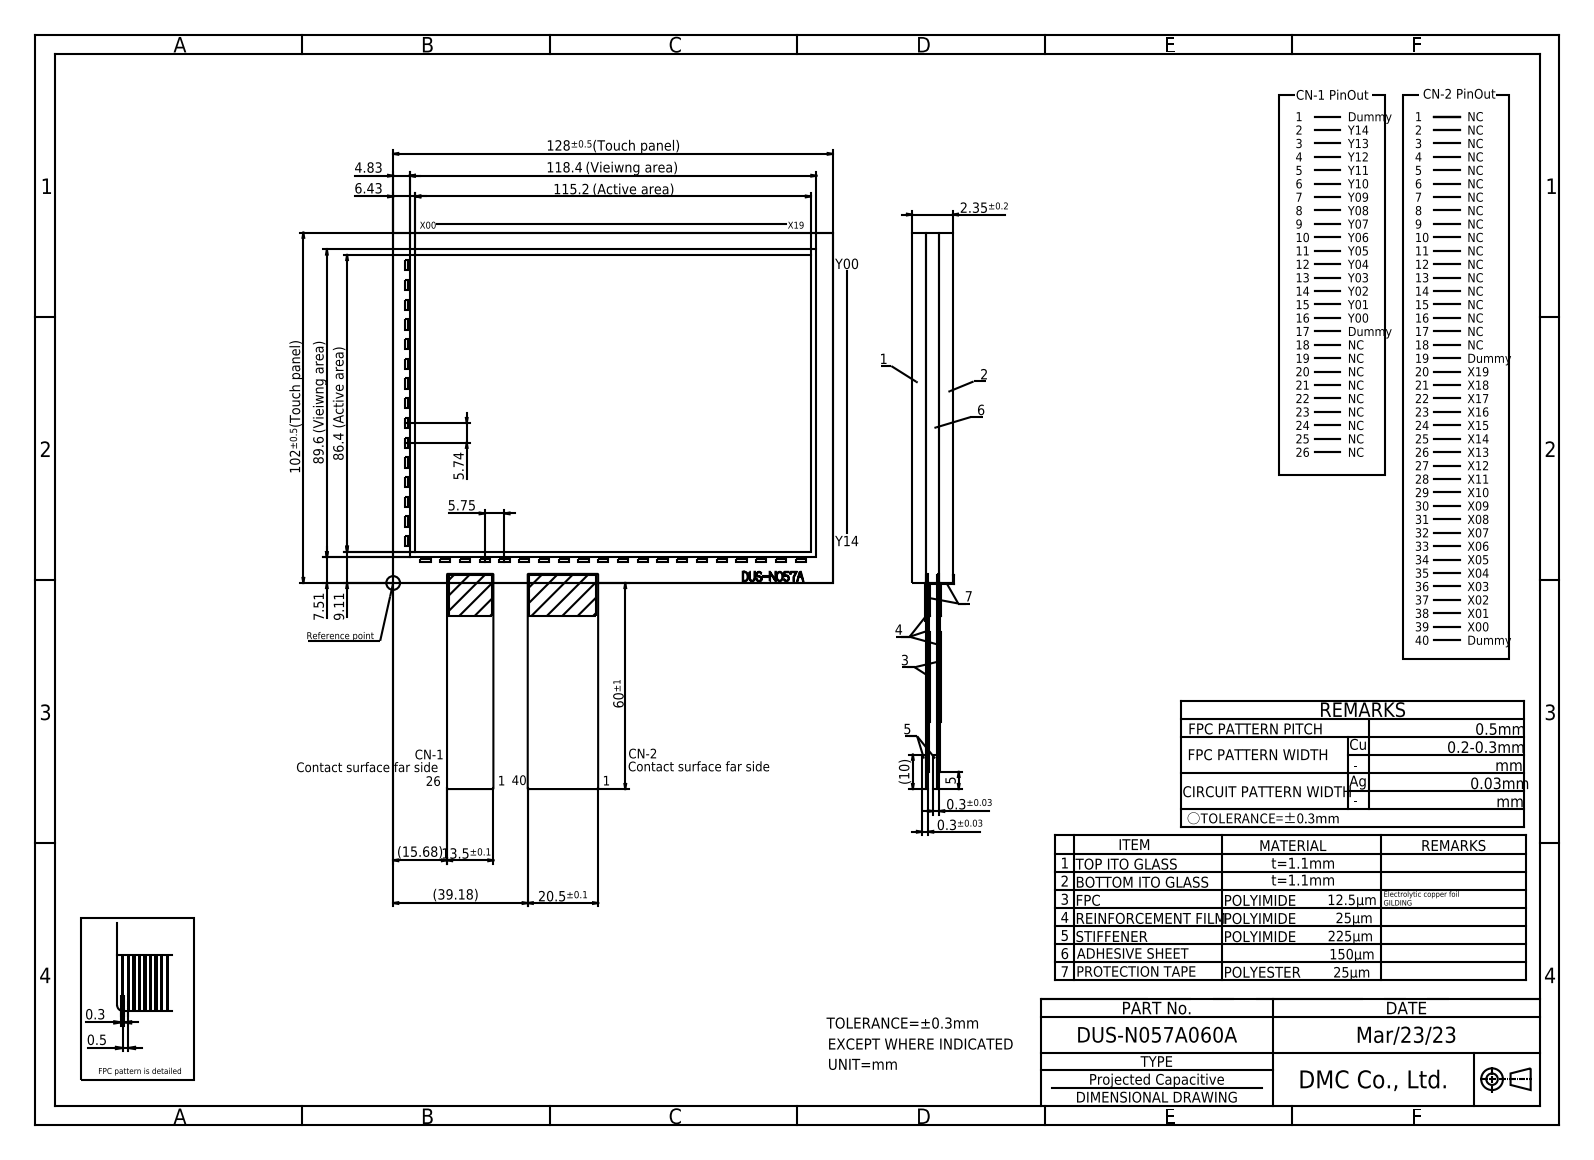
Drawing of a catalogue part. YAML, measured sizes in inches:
part_name: "DUS-N057A060A"
step_written_by: "Autodesk Inventor 2020 (AUTOMOTIVE_DESIGN)"
units: inches
bodies: {solids: 1, faces: 302, planar: 298, cylindrical: 4, other: 0}
overall_size: [7.181, 7.055, 0.093]
volume: 1.886
surface_area: 48.67
partial_cylinders:
  - {radius: 0.008, count: 4}
face_to_face_distances: [0.093, 0.043, 0.047, 0.045, 0.049, 0.039, 0.089, 0.031, 0.028, 0.061]
